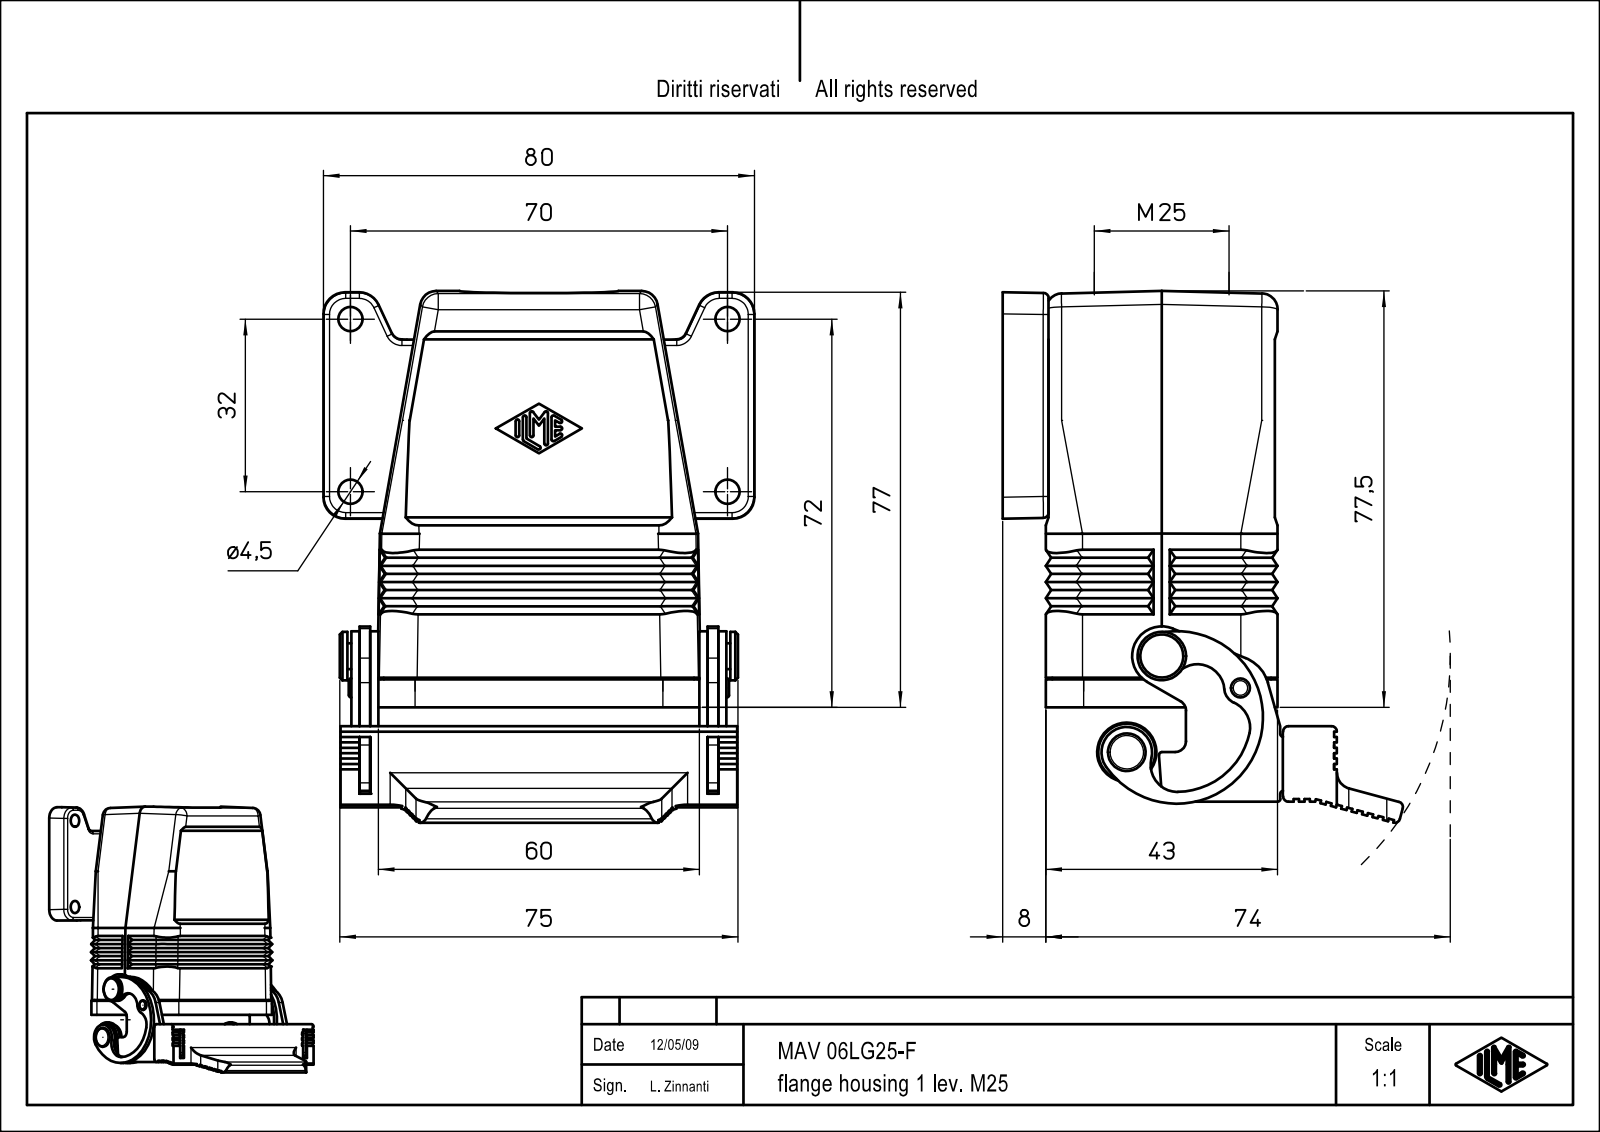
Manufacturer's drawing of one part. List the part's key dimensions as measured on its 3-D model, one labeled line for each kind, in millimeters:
Part name (STEP PRODUCT): MAV_06LG25-F
STEP written by: CoCreate Modeling 16.00A 16-Aug-2008 (C) Parametric Technology GmbH (AUTOMOTIVE_DESIGN)
Units: millimetres
Bodies: 1 solid, 1192 faces (547 planar, 398 cylindrical, 247 other)
Overall size (bounding box): 98.67 × 80 × 74.27
Volume: 86 794 mm³ · Surface area: 49 916 mm²
Round holes (diameter × count): ⌀3.5 ×4, ⌀3.3 ×3, ⌀4.5 ×3, ⌀9.5 ×3, ⌀2 ×1, ⌀3.1 ×1, ⌀4 ×1, ⌀5 ×1, ⌀25 ×1
Round bosses / shafts (diameter × count): ⌀4 ×3, ⌀3.14 ×3, ⌀11 ×1, ⌀9 ×1, ⌀7 ×1, ⌀5 ×1, ⌀3.8 ×1, ⌀3.5 ×1
Partial cylindrical surfaces — rounded edges, fillets, slot ends (radius × count): R7 ×41, R1 ×32, R3 ×26, R0.33 ×22, R4 ×8, R0.17 ×6, R0.5 ×6, R0.27 ×4
Main face-to-face distances: 0.5, 3.5, 7, 42.5, 2, 64.6, 4, 3, 50, 49.5
Hole centre spacings: 25.81, 14.14, 20, 27, 44, 51.62, 14.32, 15.75
